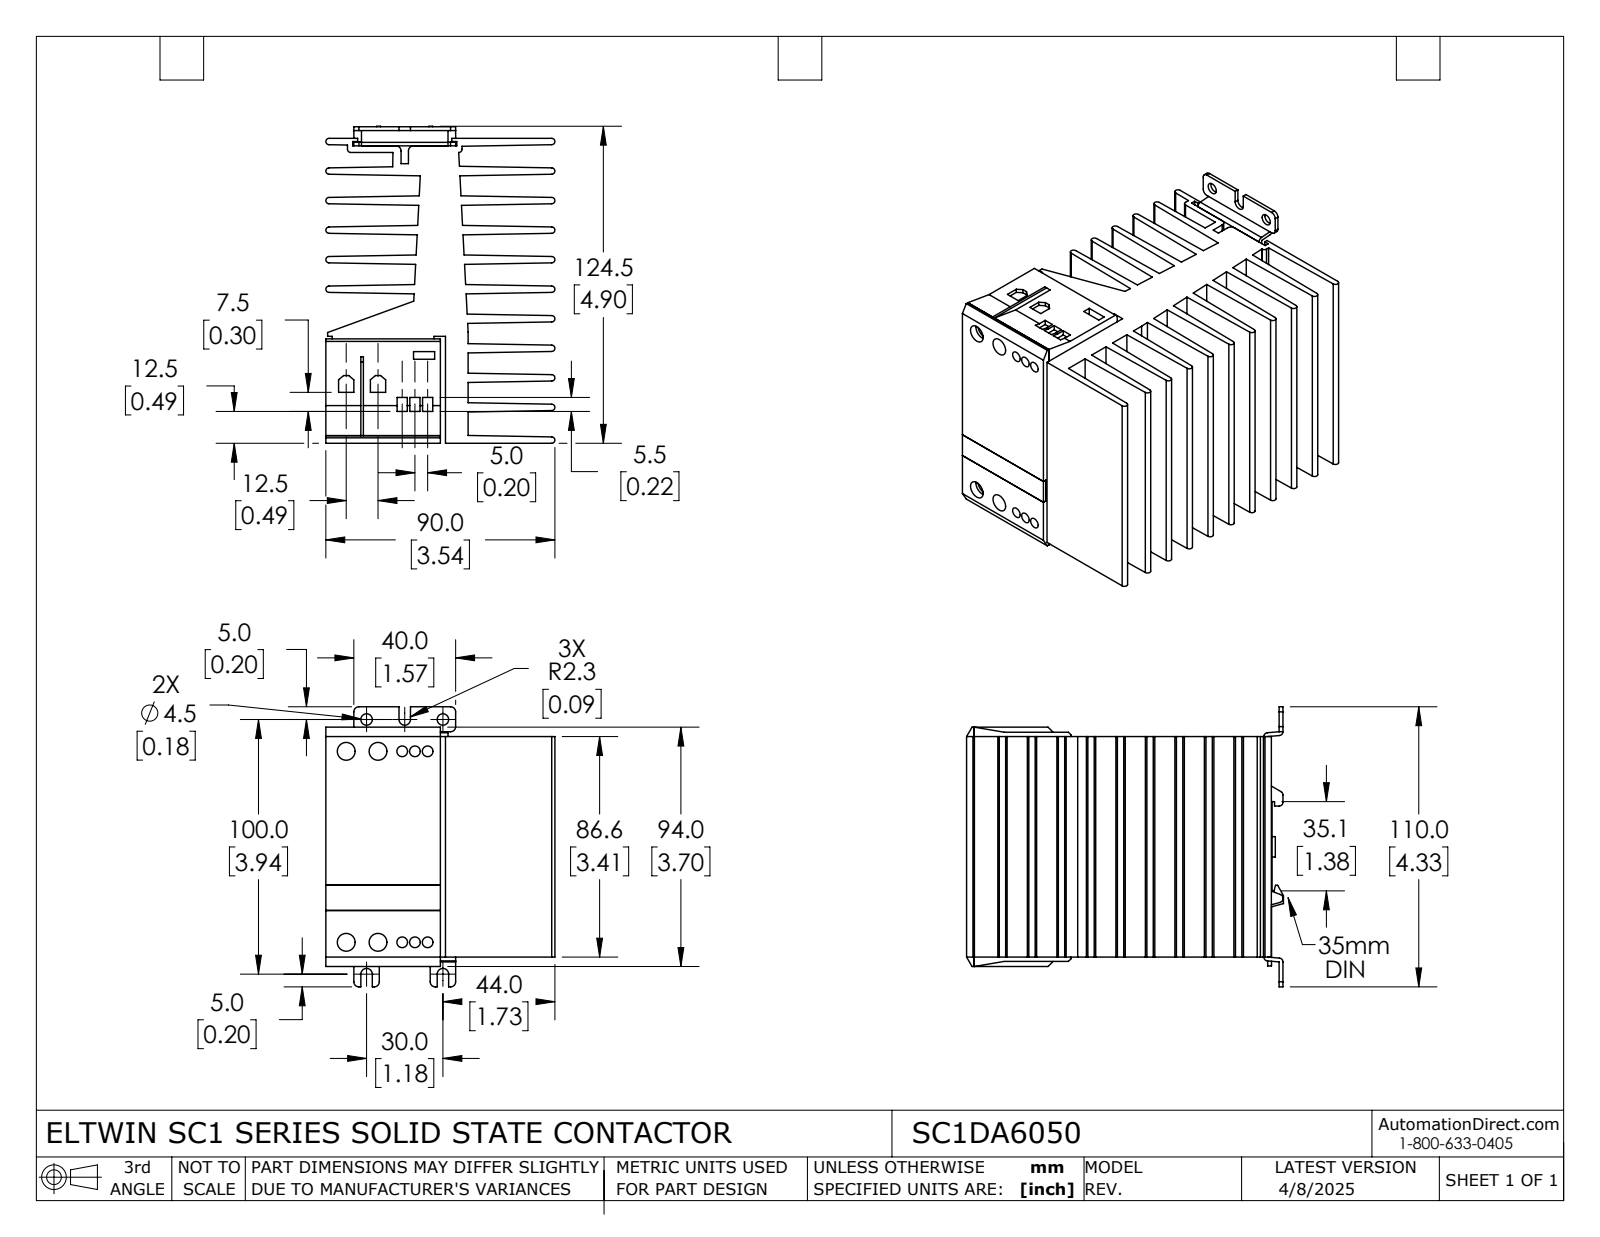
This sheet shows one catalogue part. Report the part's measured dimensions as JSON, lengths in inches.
{"part_name": "SC1DA6050", "step_written_by": "SolidWorks 2021 (AUTOMOTIVE_DESIGN)", "units": "inches", "bodies": {"solids": 7, "faces": 404, "planar": 294, "cylindrical": 110, "other": 0}, "overall_size": [4.902, 4.331, 3.543], "volume_in3": 31.2, "surface_area_in2": 277.4, "round_holes": [[0.165, 6], [0.173, 6], [0.276, 4], [0.177, 2], [0.315, 2]], "round_bosses_or_shafts": [[0.315, 3]], "partial_cylinders_radius": [[0.049, 19], [0.079, 18], [0.059, 10], [0.051, 4], [0.089, 3]], "face_to_face_distances": [0.457, 0.913, 1.37, 0.159, 0.3, 0.157, 1.827, 1.669, 1.828, 2.126], "hole_center_spacings": [2.953, 0.197, 2.959, 0.374, 0.394, 0.492, 0.571, 0.768]}
